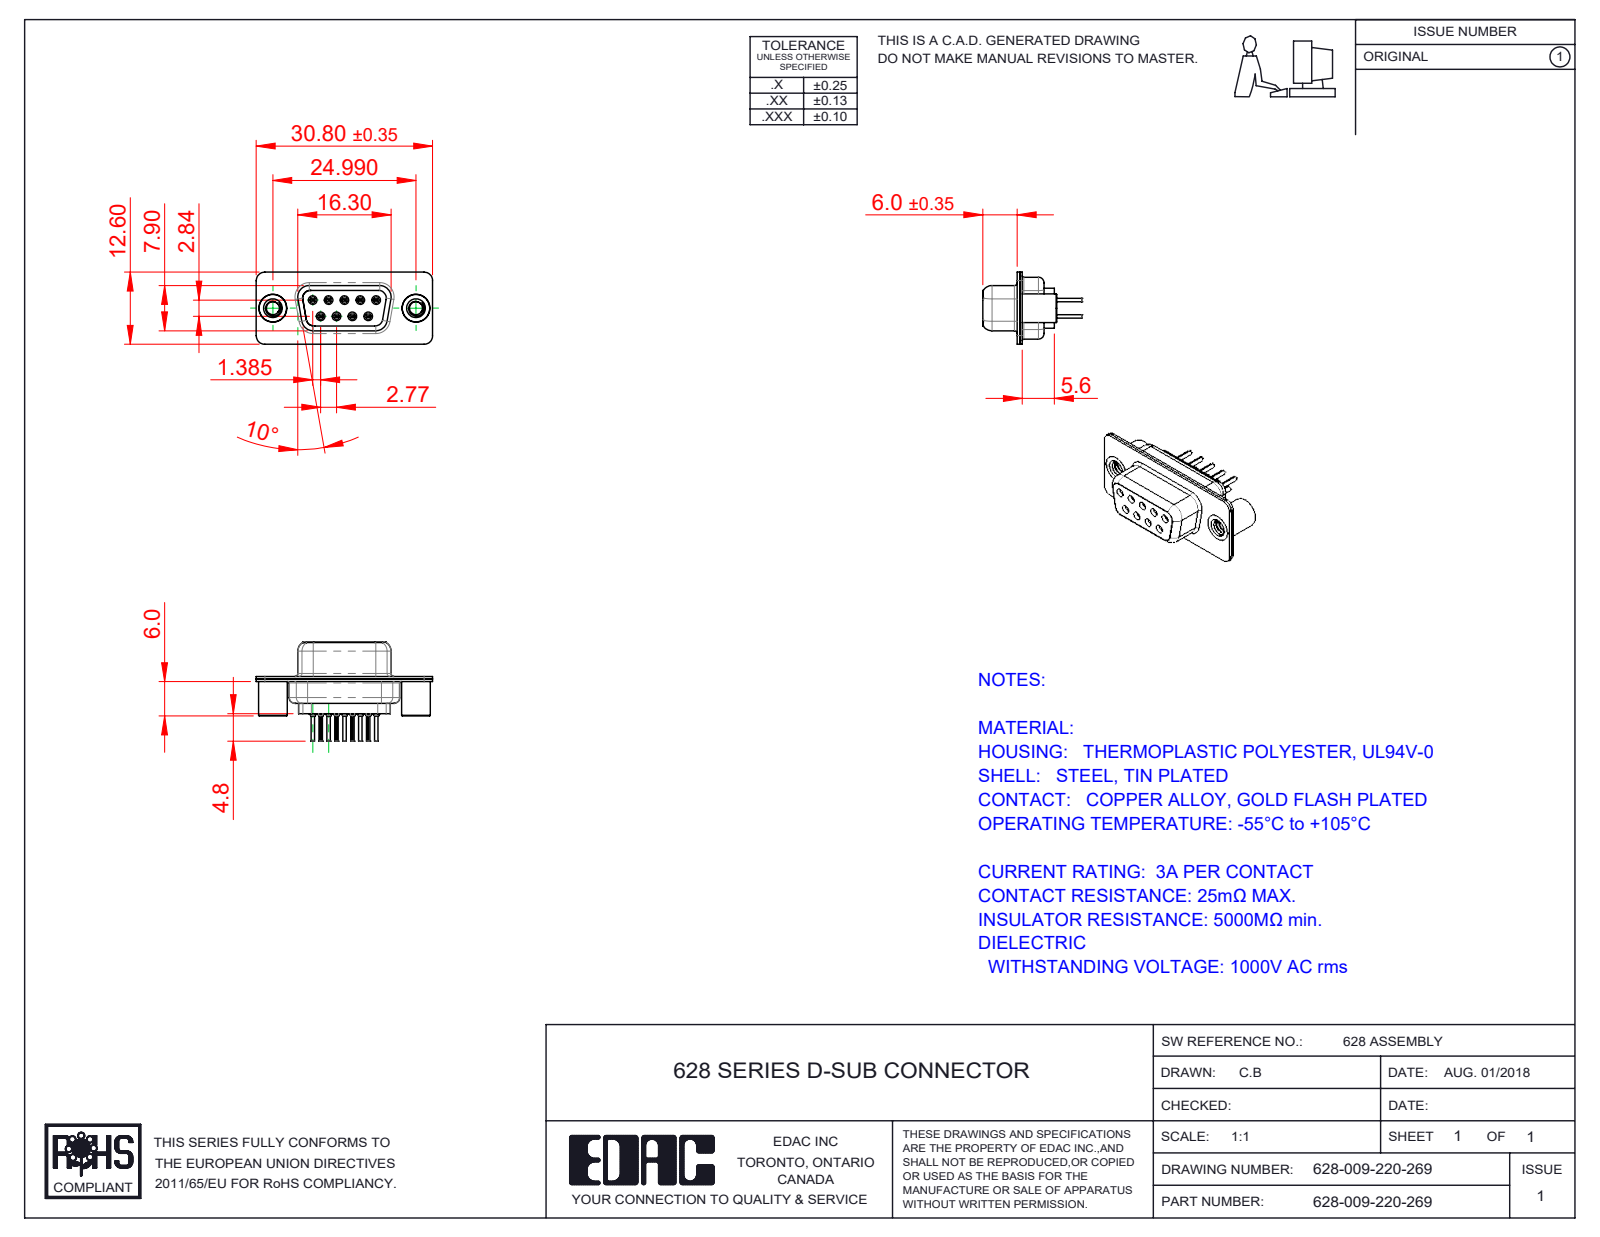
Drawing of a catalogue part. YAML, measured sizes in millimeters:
part_name: "628 Contact Row 1_20L; 628 Shell Front_09 Contacts; 628 Shell Rear_09 Contacts; 628 Housing_09 LP (+3 more)"
step_written_by: "SolidWorks 2020 (CONFIG_CONTROL_DESIGN)"
units: millimeters
bodies: {solids: 14, faces: 1444, planar: 346, cylindrical: 454, other: 644}
overall_size: [30.8, 17.3, 12.6]
volume: 1855
surface_area: 4698
round_holes:
  - {diameter: 0.2, count: 9}
  - {diameter: 0.8, count: 9}
  - {diameter: 0.9, count: 9}
  - {diameter: 1.1, count: 9}
  - {diameter: 1.6, count: 9}
  - {diameter: 1.7, count: 5}
  - {diameter: 2.26, count: 2}
  - {diameter: 4, count: 2}
  - {diameter: 4.05, count: 2}
  - {diameter: 4.85, count: 2}
round_bosses_or_shafts:
  - {diameter: 2, count: 9}
  - {diameter: 1.5, count: 9}
  - {diameter: 1.2, count: 9}
  - {diameter: 0.6, count: 9}
  - {diameter: 5, count: 2}
  - {diameter: 4.95, count: 2}
  - {diameter: 4.8, count: 2}
partial_cylinders:
  - {radius: 0.1, count: 18}
  - {radius: 1.5, count: 17}
  - {radius: 2, count: 12}
  - {radius: 0.28, count: 9}
  - {radius: 1.35, count: 6}
  - {radius: 0.25, count: 4}
  - {radius: 0.5, count: 4}
  - {radius: 0.6, count: 4}
face_to_face_distances: [0.45, 0.4, 0.9, 1.9, 8.5, 6.6, 1.4, 6.5, 0.5, 7.05]
hole_center_spacings: [3.16, 2.77, 5.54, 5.03, 5.04, 8.31, 7.48, 7.49]
